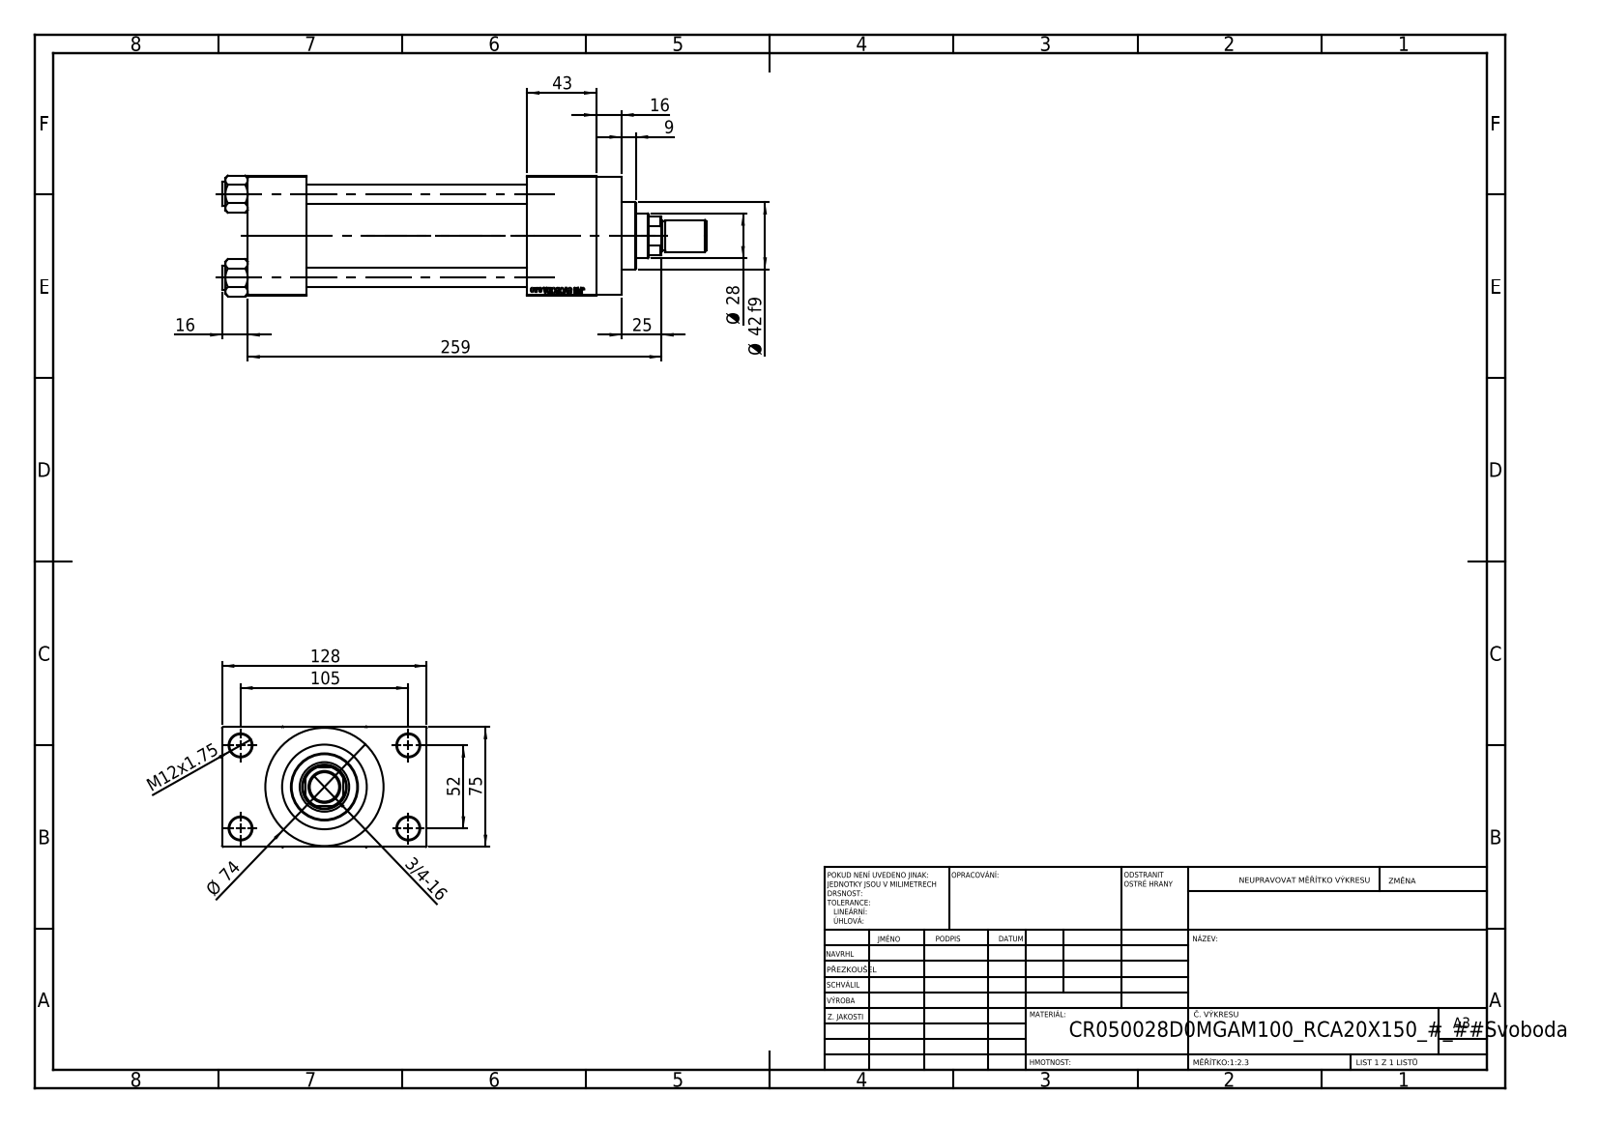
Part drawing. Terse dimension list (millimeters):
name: V215CR_D_Body; ROD_END_AH; V215CR_VCP_D; V215CR_D_TYCINKA (+2 more)
written by: SolidWorks 2019 (CONFIG_CONTROL_DESIGN)
unit: mm
bodies: 12 solids, 1118 faces (501 planar, 93 cylindrical, 524 other)
size: 303 × 128 × 75.54
volume: 949 296 mm³; area: 217 043 mm²
holes: 4× ⌀12, 4× ⌀14, 2× ⌀7, 2× ⌀20.96, 2× ⌀30, 1× ⌀18.5, 1× ⌀28, 1× ⌀31, 1× ⌀41, 1× ⌀50, 1× ⌀53
bosses: 4× ⌀15, 1× ⌀74, 1× ⌀56, 1× ⌀42, 1× ⌀20, 1× ⌀18
rounds: 1× R13.5
face distances: 75, 138, 37, 175, 26.5, 101.5, 218, 181, 43, 16
hole spacings: 26.35, 36.98, 52.3, 58.43, 58.59, 78.65, 94.37, 52
